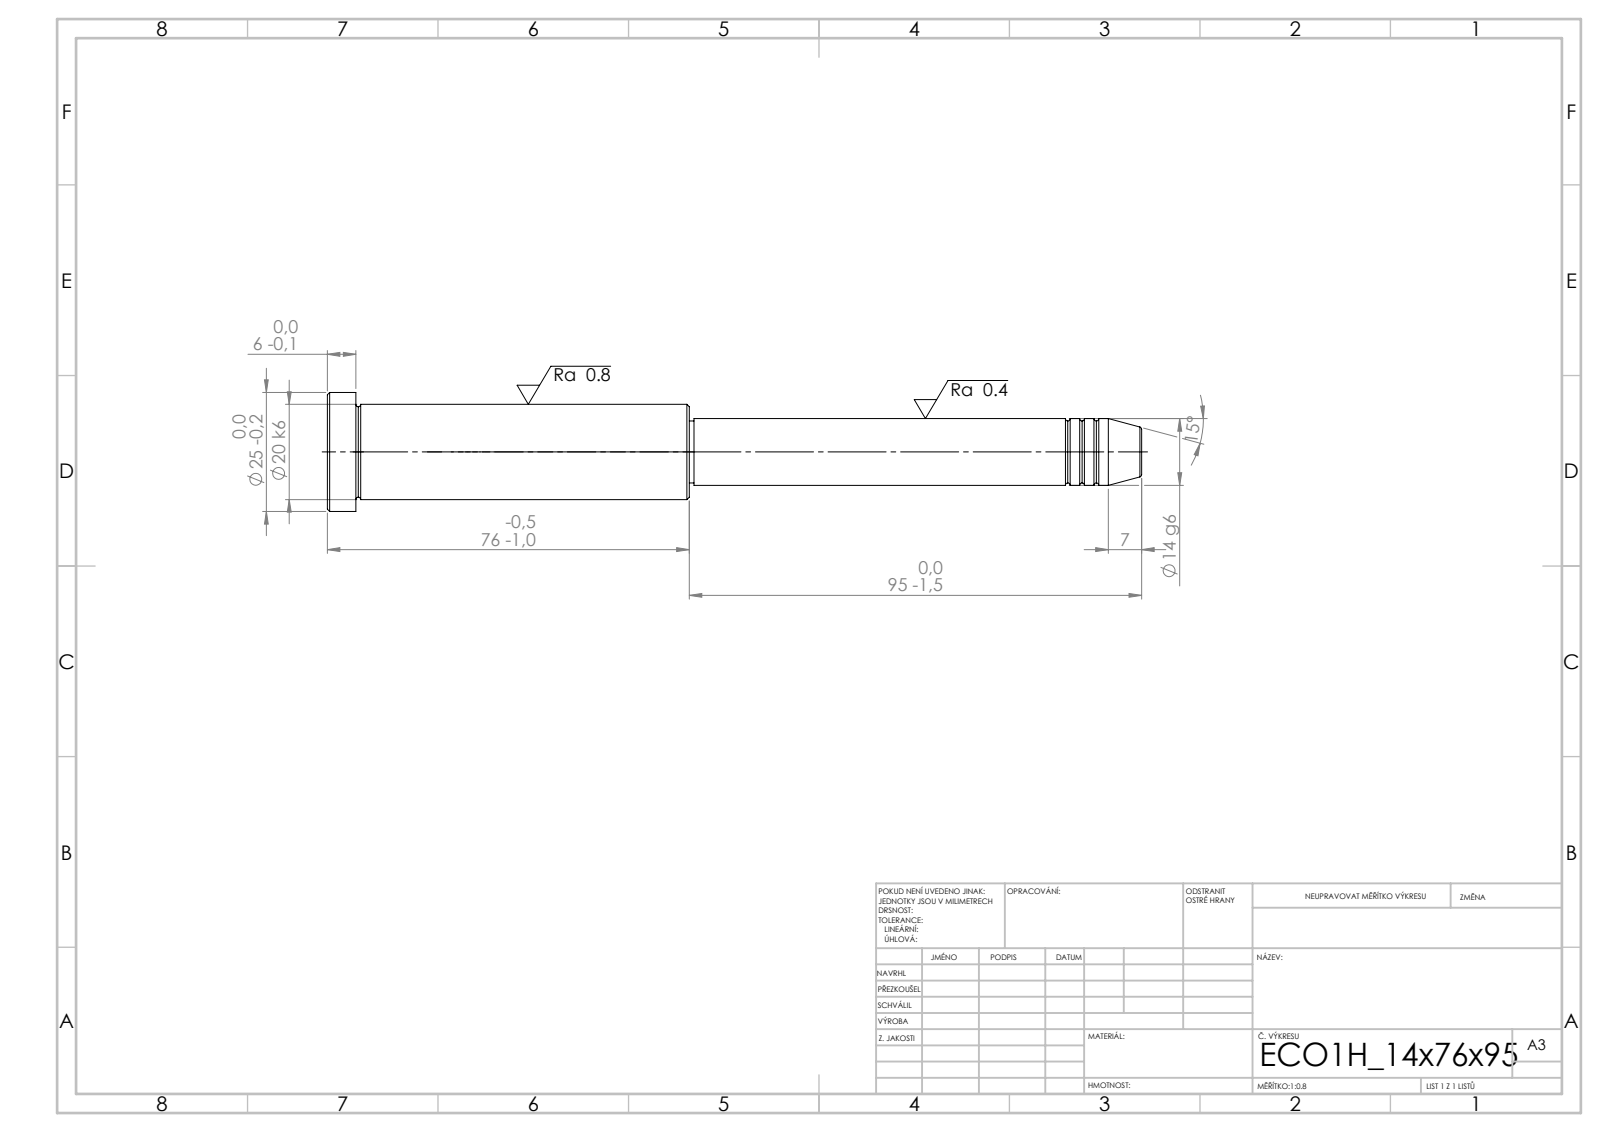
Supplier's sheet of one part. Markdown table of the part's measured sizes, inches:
| quantity | value |
| --- | --- |
| STEP written by | SolidWorks 2019 (CONFIG_CONTROL_DESIGN) |
| units | inches |
| bodies | 1 solid, 43 faces (5 planar, 14 cylindrical, 24 other) |
| overall size | 6.732 × 0.984 × 0.984 |
| volume | 2.391 in³ |
| surface area | 15.53 in² |
| round bosses / shafts (diameter × count) | 0.984 × 1, 0.787 × 1, 0.551 × 1, 0.512 × 1 |
| main face-to-face distances | 0.236, 2.756, 2.992, 3.74, 6.496, 6.732, 3.701, 0.039, 2.795, 3.031 |
